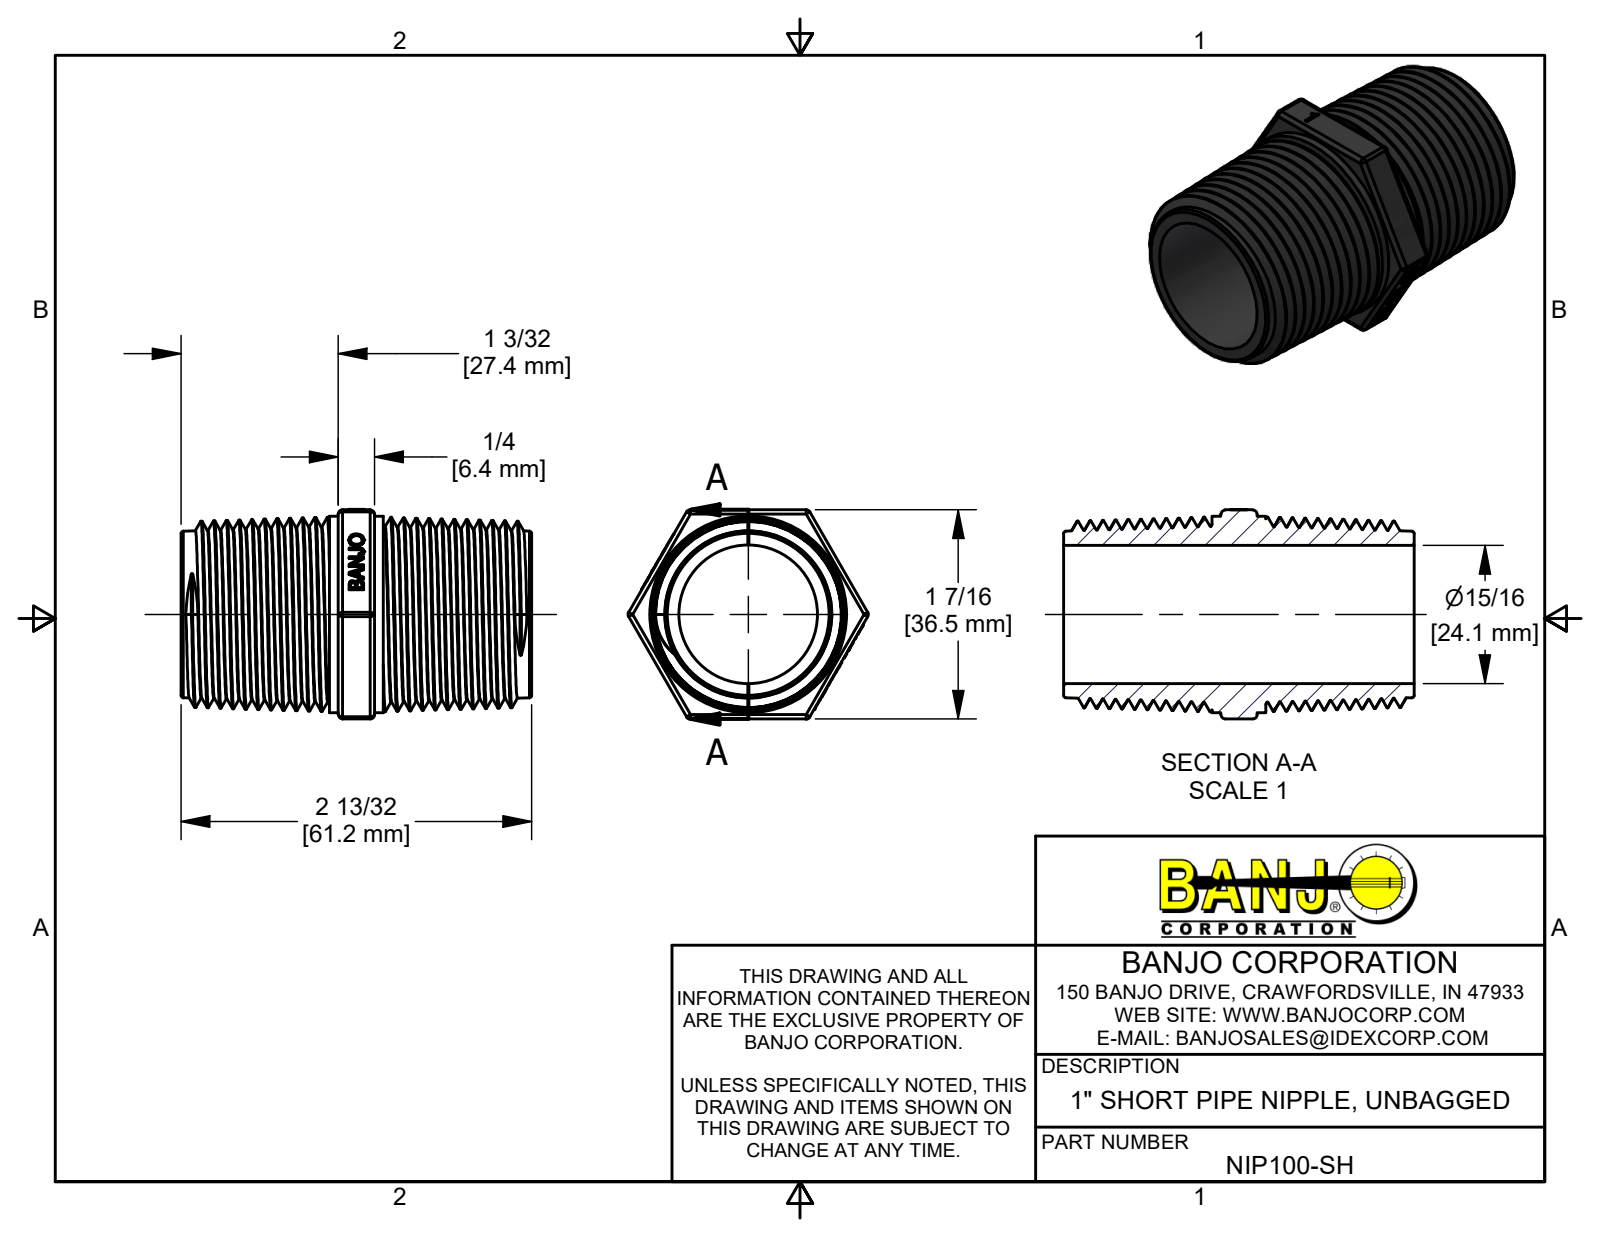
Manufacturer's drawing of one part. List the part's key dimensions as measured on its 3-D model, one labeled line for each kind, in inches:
Part name (STEP PRODUCT): NIP100-SH; NIP100-SHU
STEP written by: Autodesk Inventor 2022 (AUTOMOTIVE_DESIGN)
Units: inches
Bodies: 1 solid, 267 faces (124 planar, 21 cylindrical, 122 other)
Overall size (bounding box): 2.41 × 1.651 × 1.441
Volume: 1.367 in³ · Surface area: 24.82 in²
Round holes (diameter × count): ⌀0.95 ×1
Round bosses / shafts (diameter × count): ⌀1.35 ×1
Partial cylindrical surfaces — rounded edges, fillets, slot ends (radius × count): R0.03 ×18
Main face-to-face distances: 1.438, 1.08, 1.33, 1.02, 1.39, 0.06, 0.31, 2.41, 0.25, 0.37
